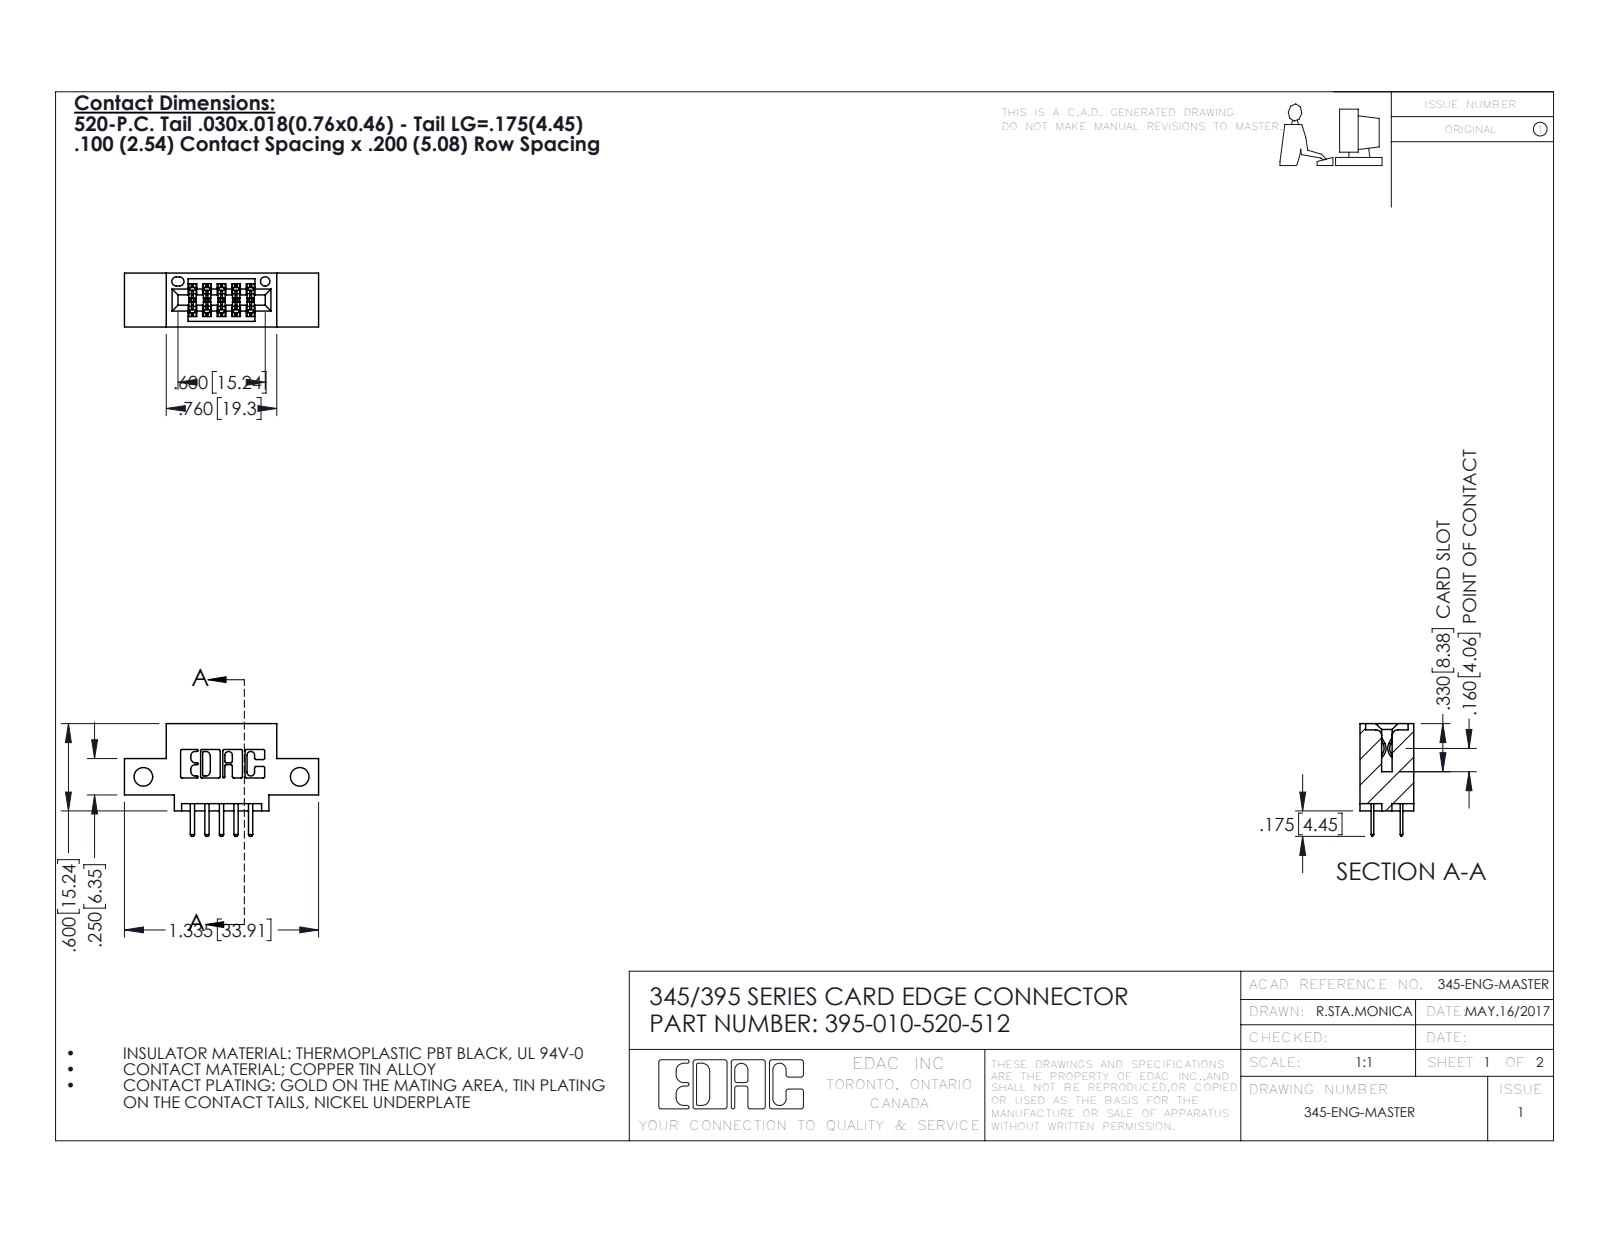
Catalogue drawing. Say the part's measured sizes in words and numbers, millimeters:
The part is named "345 Part_0.110 Offset - Side Mount; 345-292-001_345-293-120; 395-010-520-512". Its 3-D file was written by "SolidWorks 2016 (CONFIG_CONTROL_DESIGN)". It is 11 solids with 670 faces: 434 planar, 236 cylindrical and 0 other. Overall it measures 33.9 by 19.7 by 9.4 millimeters. Its volume is 2 790 cubic millimeters and its surface area 3 348 square millimeters. Round holes: 2 of diameter 3.3, 1 of diameter 1.6. Partial cylindrical surfaces (rounded edges, fillets, slot ends): 22 of radius 0.3, 15 of radius 0.2, 14 of radius 0.3, 6 of radius 0.2, 6 of radius 0.8, 3 of radius 0.7, 2 of radius 0.4, 2 of radius 0.5. The main face-to-face distances are 5.1, 9.4, 7.6, 1.8, 2.5, 6.4, 0.6, 2.5, 6.9, 1.5. The hole center spacings are 27.3.
